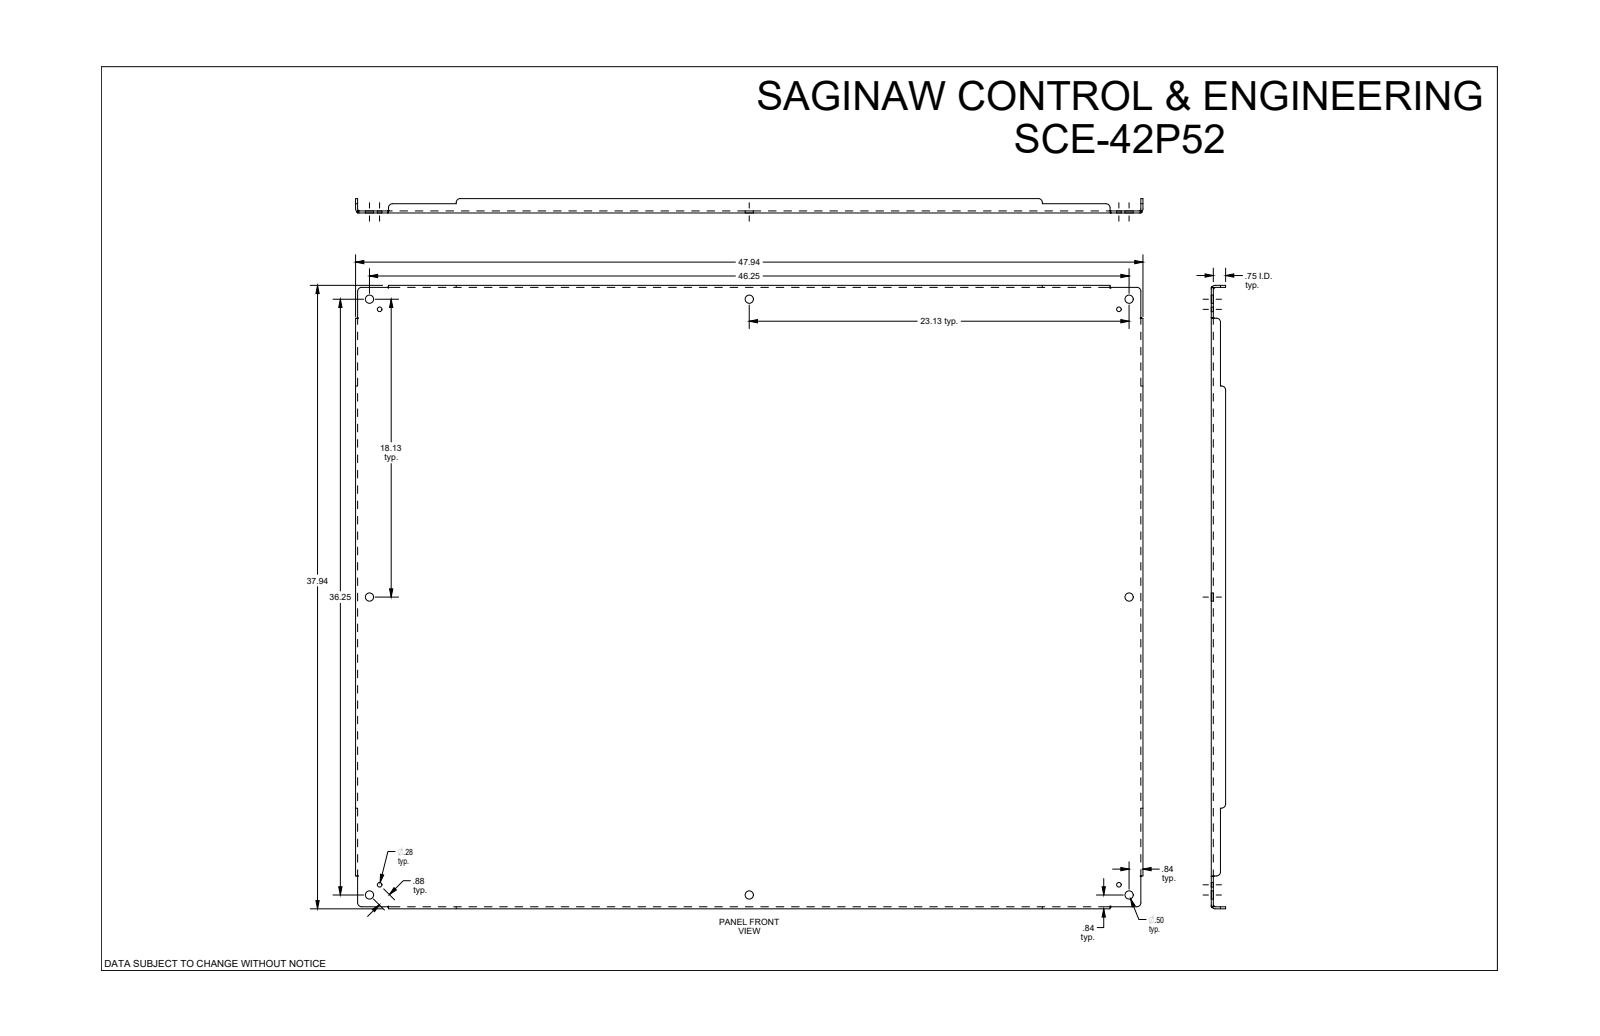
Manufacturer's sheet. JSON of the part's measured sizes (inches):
{"part_name": "SCE-42P52", "step_written_by": "SolidWorks 2019 (CONFIG_CONTROL_DESIGN)", "units": "inches", "bodies": {"solids": 1, "faces": 110, "planar": 46, "cylindrical": 40, "other": 24}, "overall_size": [47.938, 37.938, 0.875], "volume_in3": 238.7, "surface_area_in2": 3843, "round_holes": [[0.5, 8], [0.281, 4]], "partial_cylinders_radius": [[0.25, 12], [0.112, 4], [0.237, 4]], "face_to_face_distances": [0.125, 0.125, 37.813, 47.813, 37.687, 37.938, 47.687, 47.938, 0.75, 0.875], "hole_center_spacings": [0.875, 17.517, 18.125, 22.515, 23.125, 29.382, 35.637, 42.144]}
